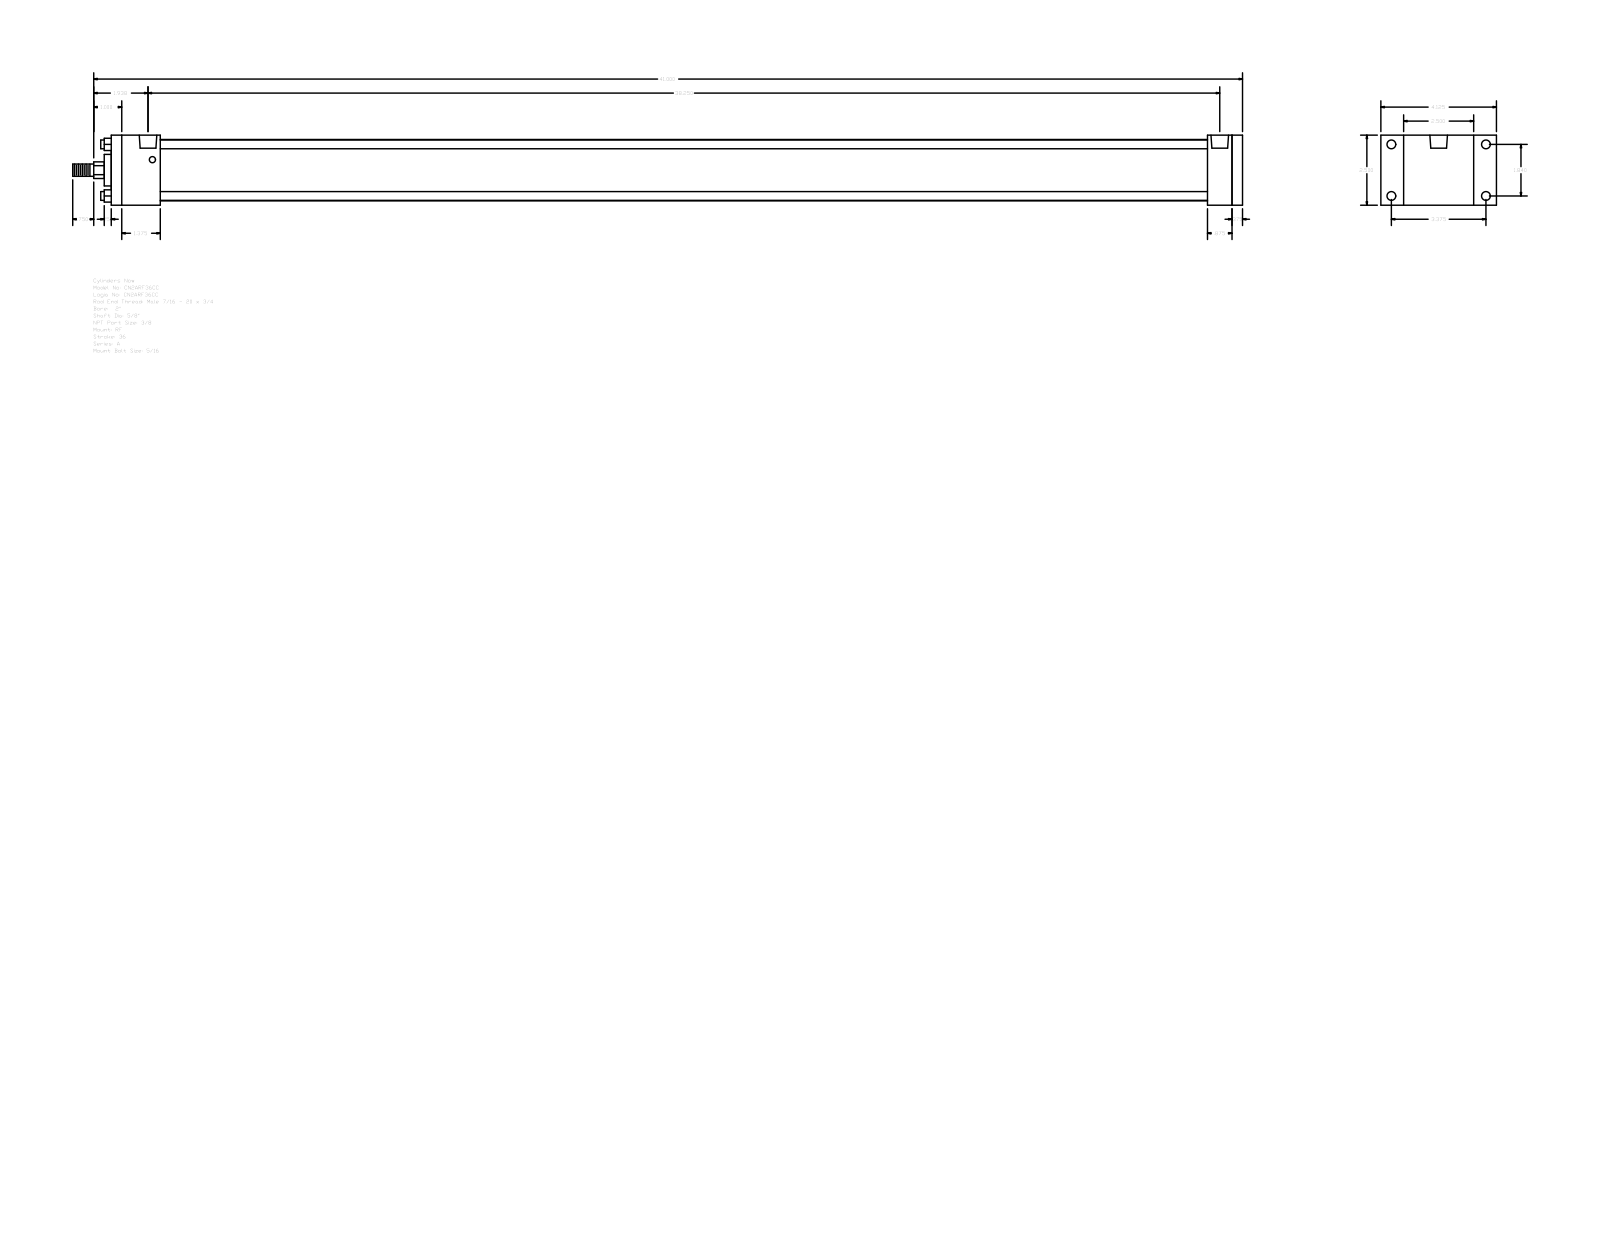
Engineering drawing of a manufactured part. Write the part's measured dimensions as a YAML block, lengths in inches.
part_name: "A_RF__0200_0.625"
step_written_by: "GSSL Pune (CONFIG_CONTROL_DESIGN)"
units: inches
bodies: {solids: 0, faces: 92, planar: 64, cylindrical: 28, other: 0}
overall_size: [41.75, 4.125, 2.5]
round_holes:
  - {diameter: 0.219, count: 4}
  - {diameter: 0.313, count: 4}
  - {diameter: 0.627, count: 2}
round_bosses_or_shafts:
  - {diameter: 0.313, count: 4}
  - {diameter: 2.19, count: 1}
  - {diameter: 1.125, count: 1}
  - {diameter: 0.625, count: 1}
  - {diameter: 0.437, count: 1}
partial_cylinders:
  - {radius: 0.297, count: 1}
face_to_face_distances: [2.5, 40.375, 40, 0.375, 1.75, 38.25, 38.625, 39.125, 37.375, 0.875]
hole_center_spacings: [1.84, 3.375, 3.844, 37.937, 0.156, 0.157, 38.093, 38.094]
